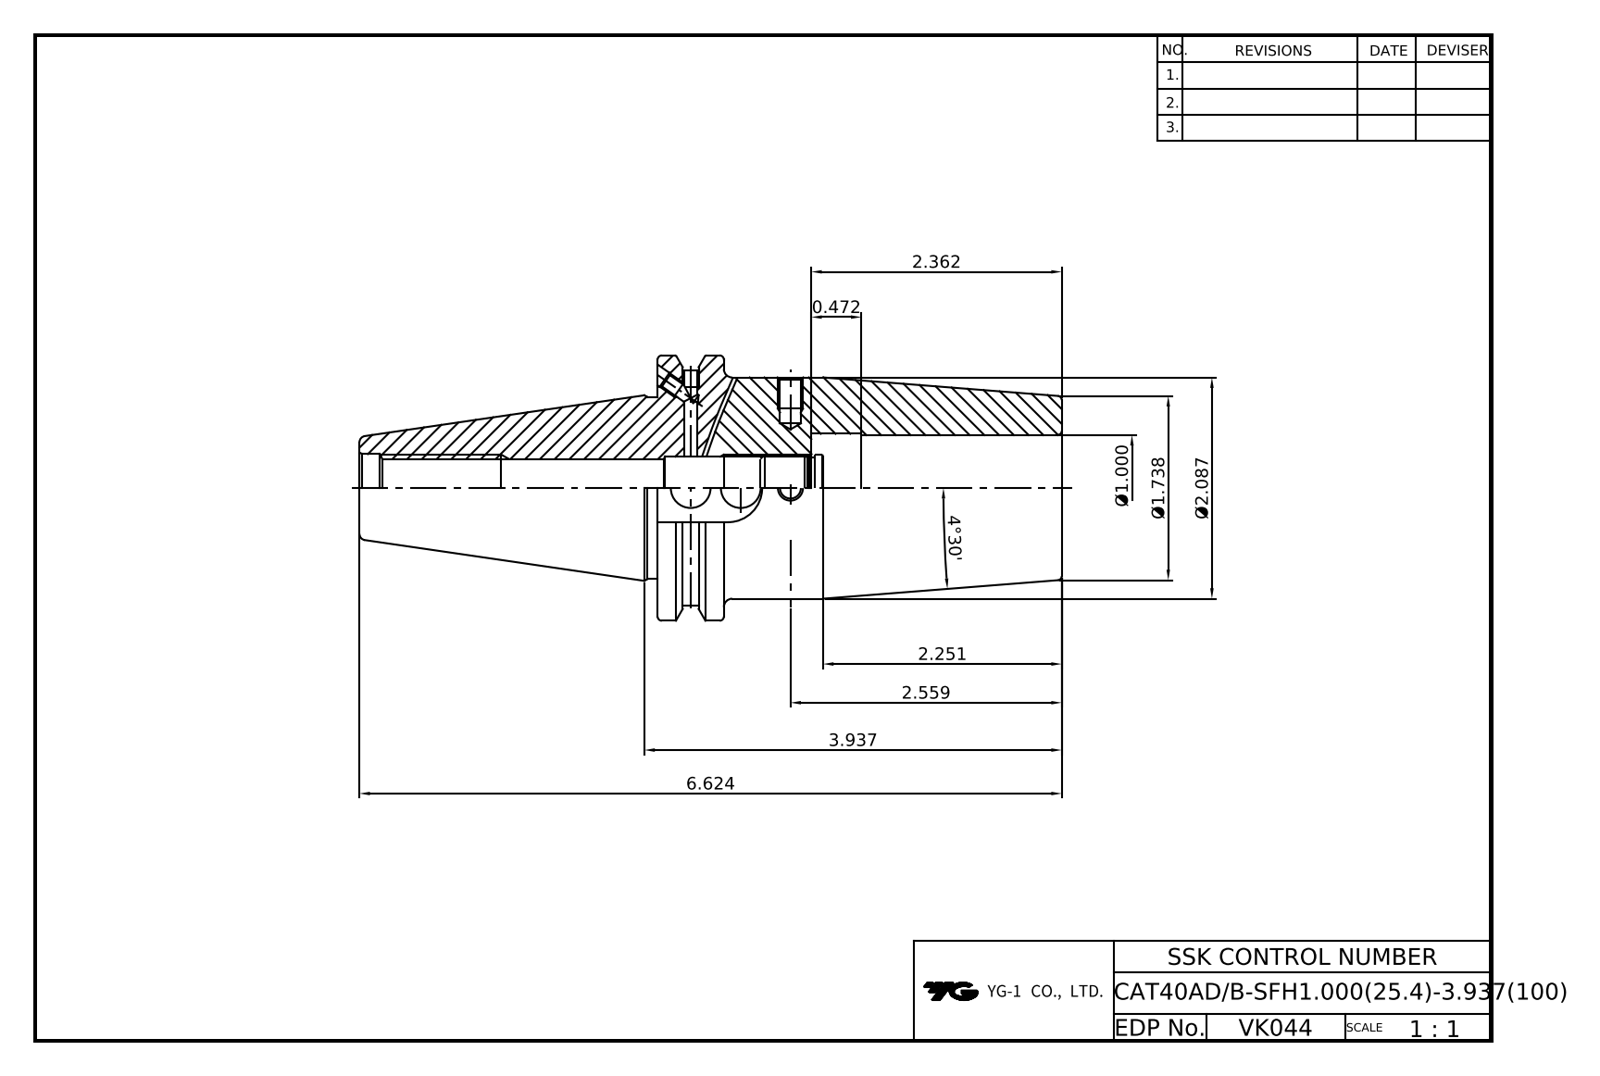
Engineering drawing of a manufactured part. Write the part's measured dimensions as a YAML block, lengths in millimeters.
part_name: "LO-CAT40ADB-SFH25.4-100"
step_written_by: "Autodesk Inventor 2022 (AUTOMOTIVE_DESIGN)"
units: millimeters
bodies: {solids: 1, faces: 87, planar: 34, cylindrical: 31, other: 22}
overall_size: [168.25, 63.5, 61.09]
volume: 223354
surface_area: 38658
round_holes:
  - {diameter: 3.24, count: 4}
  - {diameter: 4, count: 2}
  - {diameter: 4.2, count: 2}
  - {diameter: 9.53, count: 1}
  - {diameter: 13, count: 1}
  - {diameter: 13.39, count: 1}
  - {diameter: 14.92, count: 1}
  - {diameter: 16.3, count: 1}
  - {diameter: 25.4, count: 1}
  - {diameter: 26.6, count: 1}
round_bosses_or_shafts:
  - {diameter: 63.5, count: 1}
  - {diameter: 53, count: 1}
  - {diameter: 43.6, count: 1}
partial_cylinders:
  - {radius: 8.19, count: 1}
  - {radius: 28.15, count: 1}
face_to_face_distances: [96.83, 36.83, 60, 15.88, 20.95, 80.95, 47.6, 16.38, 71.42, 87.3]
